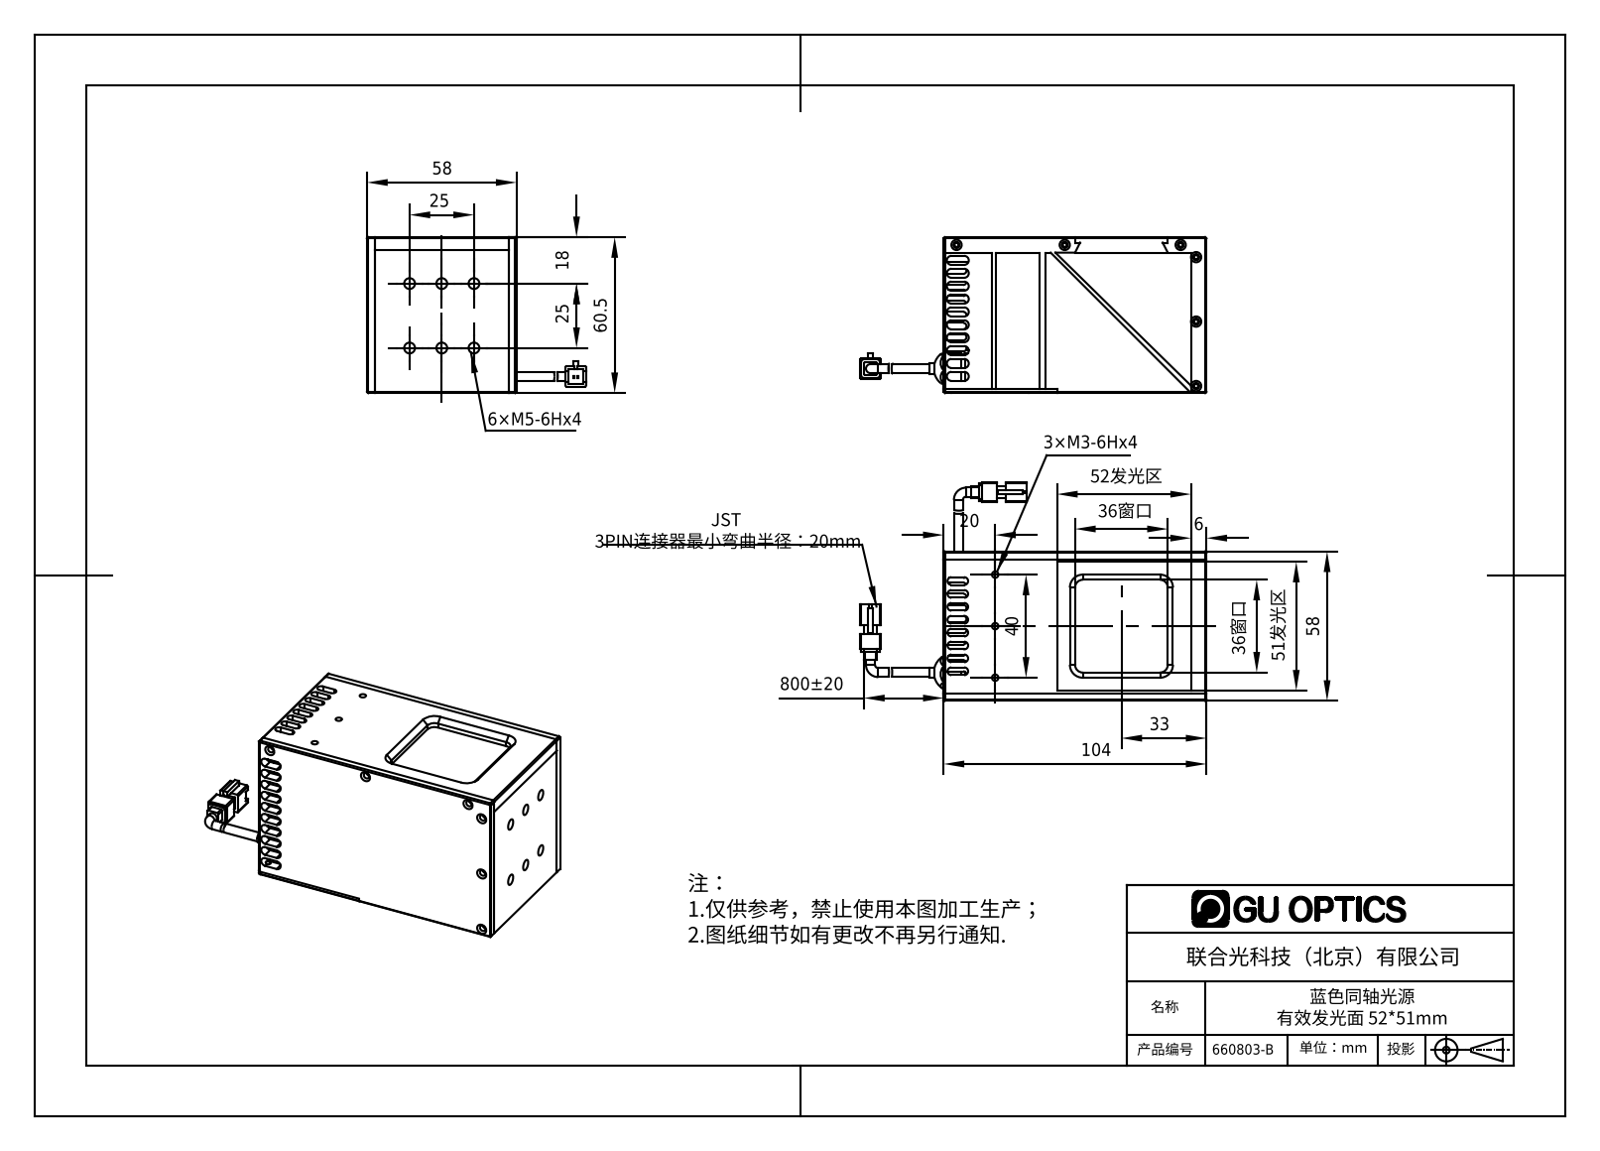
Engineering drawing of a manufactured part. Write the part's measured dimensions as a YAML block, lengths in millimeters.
part_name: "蓝色同轴光源 有效发光面 5251mm"
step_written_by: "SolidWorks 2016 (AUTOMOTIVE_DESIGN)"
units: millimeters
bodies: {solids: 22, faces: 1568, planar: 921, cylindrical: 491, other: 156}
overall_size: [134.4, 60.7, 58]
volume: 118035
surface_area: 91224
round_holes:
  - {diameter: 1.6, count: 13}
  - {diameter: 2, count: 10}
  - {diameter: 2.4, count: 10}
  - {diameter: 4, count: 6}
  - {diameter: 4.2, count: 6}
  - {diameter: 2.2, count: 5}
  - {diameter: 2.5, count: 3}
  - {diameter: 6.8, count: 1}
round_bosses_or_shafts:
  - {diameter: 3.5, count: 2}
  - {diameter: 9.76, count: 1}
  - {diameter: 8, count: 1}
  - {diameter: 4, count: 1}
partial_cylinders:
  - {radius: 1.25, count: 20}
  - {radius: 1.75, count: 20}
  - {radius: 1.5, count: 16}
  - {radius: 0.5, count: 8}
  - {radius: 1, count: 4}
  - {radius: 3, count: 4}
  - {radius: 4, count: 1}
  - {radius: 6.25, count: 1}
face_to_face_distances: [4, 54, 2, 55, 1, 58, 3, 51, 58.5, 6]
hole_center_spacings: [25, 12.5, 20, 27.95, 30, 3.58, 5.51, 9.03]
